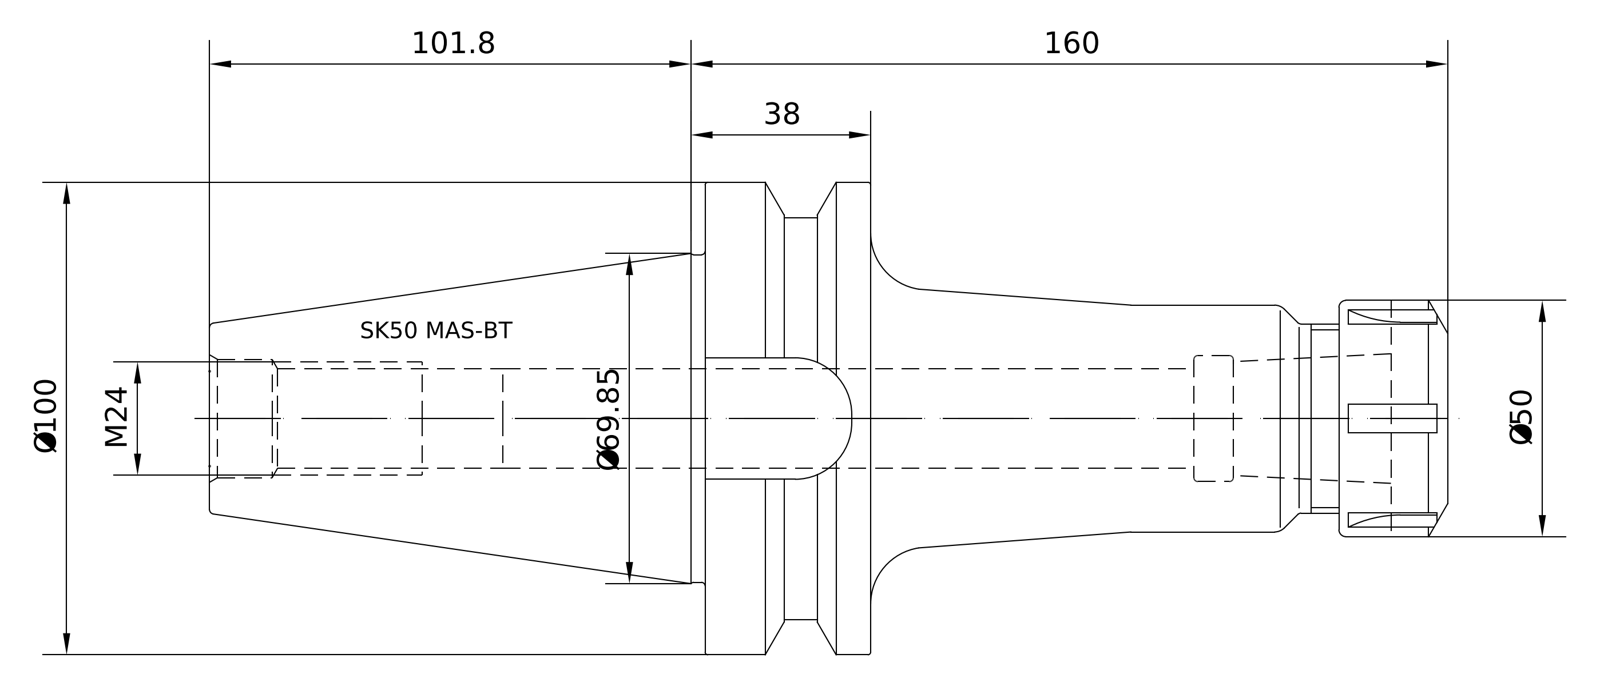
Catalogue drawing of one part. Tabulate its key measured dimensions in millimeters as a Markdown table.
| quantity | value |
| --- | --- |
| part name | 50-522-32; 83-912-32; 50-522-32_ASM |
| STEP written by | PRO/ENGINEER BY PARAMETRIC TECHNOLOGY CORPORATION, 2010430 (CONFIG_CONTROL_DESIGN) |
| units | millimeters |
| bodies | 2 solids, 148 faces (52 planar, 32 cylindrical, 64 other) |
| overall size | 261.8 × 99.97 × 99.97 |
| volume | 686 247 mm³ |
| surface area | 77 641 mm² |
| round holes (diameter × count) | 20.75 × 1, 23.5 × 1, 25.02 × 1, 25.7 × 1 |
| round bosses / shafts (diameter × count) | 99.97 × 1, 84.75 × 1, 69.15 × 1, 50 × 1, 48 × 1, 40 × 1, 24.01 × 1 |
| partial cylindrical surfaces (radius × count) | 2.7 × 6, 12.9 × 1 |
| main face-to-face distances | 35, 134.5, 99.5, 157, 122, 22.5, 70.4, 104.8, 139.8, 239.3 |
